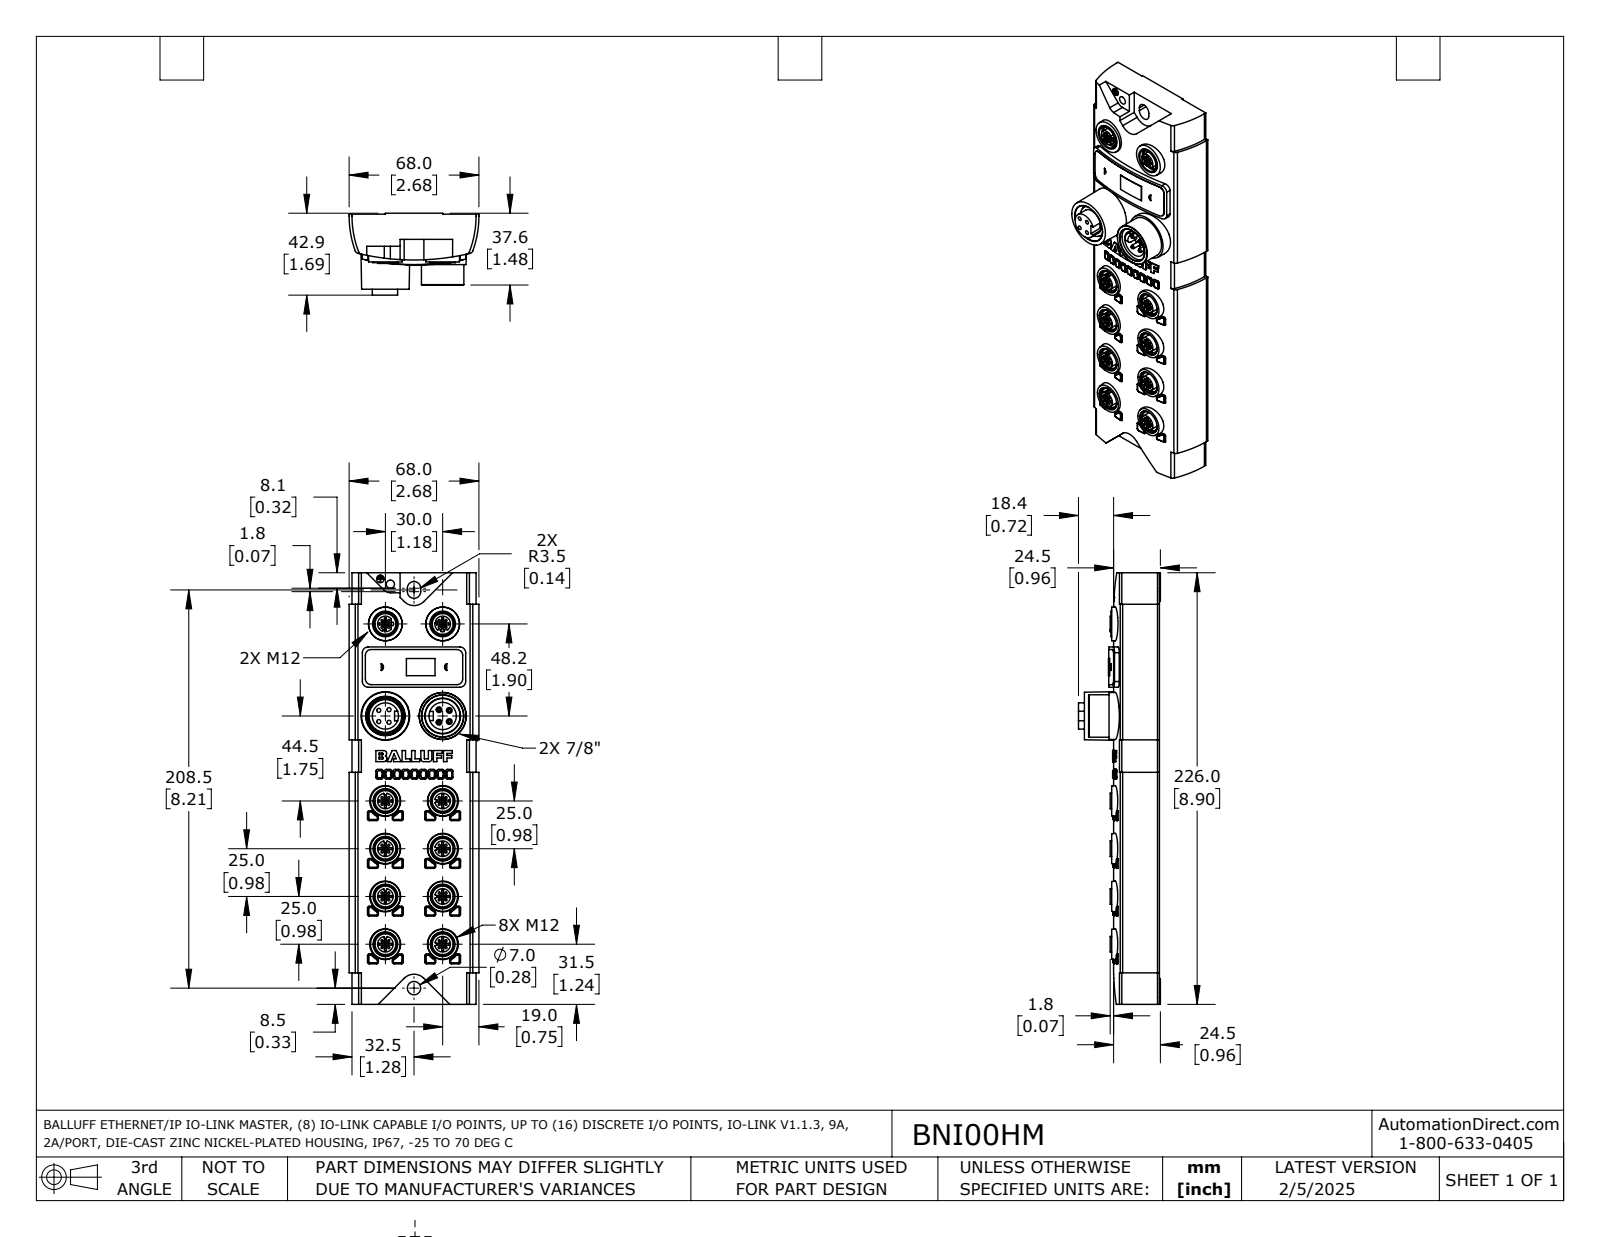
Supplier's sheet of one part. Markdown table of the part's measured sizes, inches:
| quantity | value |
| --- | --- |
| part name | BNI00HM |
| STEP written by | SolidWorks 2021 (AUTOMOTIVE_DESIGN) |
| units | inches |
| bodies | 1 solid, 1371 faces (596 planar, 686 cylindrical, 89 other) |
| overall size | 8.898 × 2.677 × 1.689 |
| volume | 20.64 in³ |
| surface area | 87.08 in² |
| round holes (diameter × count) | 0.043 × 50, 0.43 × 10, 0.484 × 8, 0.083 × 4, 0.472 × 2, 0.157 × 1, 0.169 × 1, 0.276 × 1, 0.563 × 1, 0.72 × 1, 0.798 × 1 |
| round bosses / shafts (diameter × count) | 0.323 × 9, 0.118 × 4, 0.078 × 4, 0.528 × 2, 0.875 × 1, 0.709 × 1, 0.541 × 1, 0.394 × 1 |
| partial cylindrical surfaces (radius × count) | 0.012 × 80, 0.035 × 80, 0.037 × 72, 0.039 × 40, 0.008 × 16, 0.028 × 8, 0.118 × 8, 0.34 × 8 |
| main face-to-face distances | 8.898, 0.984, 0.52, 0.465, 0.665, 0.146, 0.319, 0.35, 0.685, 1.016 |
| hole center spacings | 0.098, 0.139, 1.969, 1.181, 0.197, 1.114, 1.253, 2.296 |
